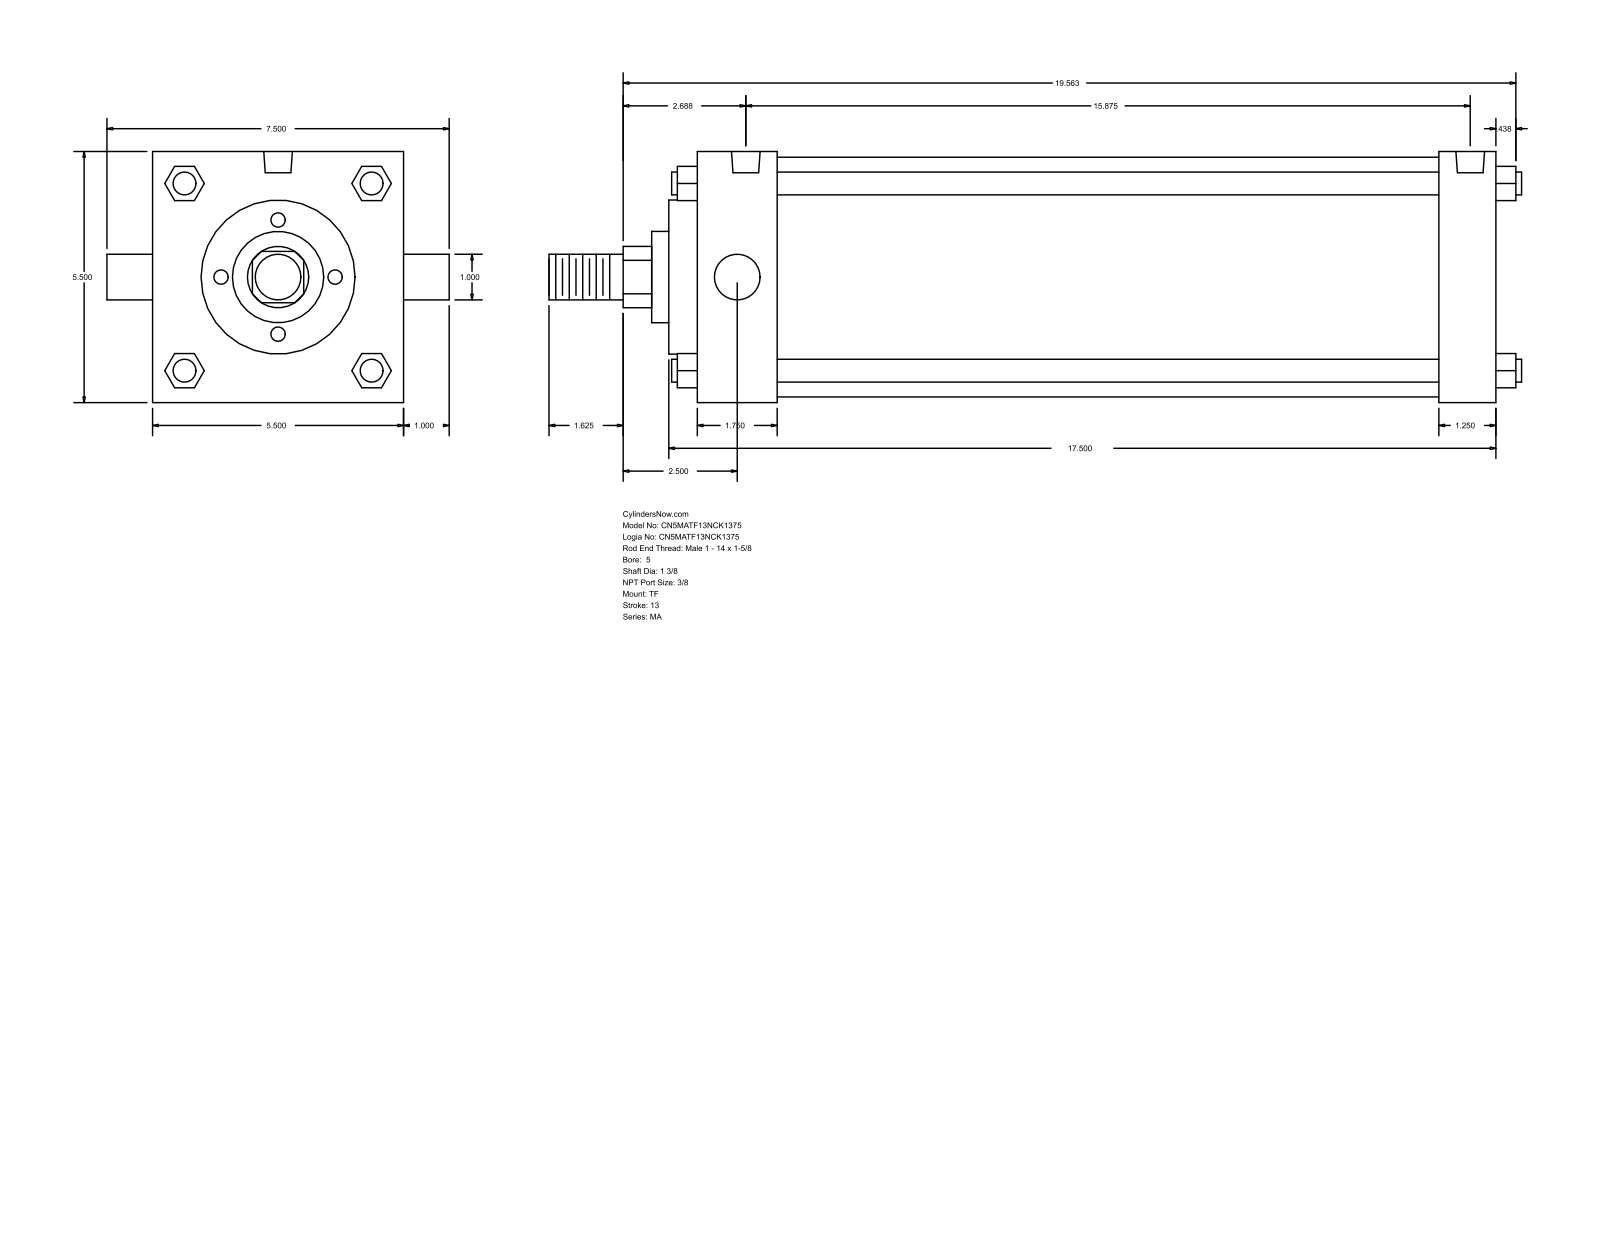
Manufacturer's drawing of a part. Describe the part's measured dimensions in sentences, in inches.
The part is named "MA_TF__0500_1.375". Its 3-D file was written by "GSSL Pune (CONFIG_CONTROL_DESIGN)". It is 0 solids with 122 faces: 93 planar, 29 cylindrical and 0 other. Overall it measures 21.313 by 7.5 by 5.5 inches. Round holes: 3 of diameter 0.437, 2 of diameter 0.627. Round bosses or shafts: 4 of diameter 0.5, 2 of diameter 1, 1 of diameter 5.25, 1 of diameter 3.375, 1 of diameter 2, 1 of diameter 1.375. Partial cylindrical surfaces (rounded edges, fillets, slot ends): 1 of radius 0.672. The main face-to-face distances are 5.5, 17.5, 16.25, 1.25, 1.75, 14.5, 15.75, 0.625, 2.375, 16.875. The hole center spacings are 0.187, 0.188, 15.5, 15.687, 15.688, 15.875.
